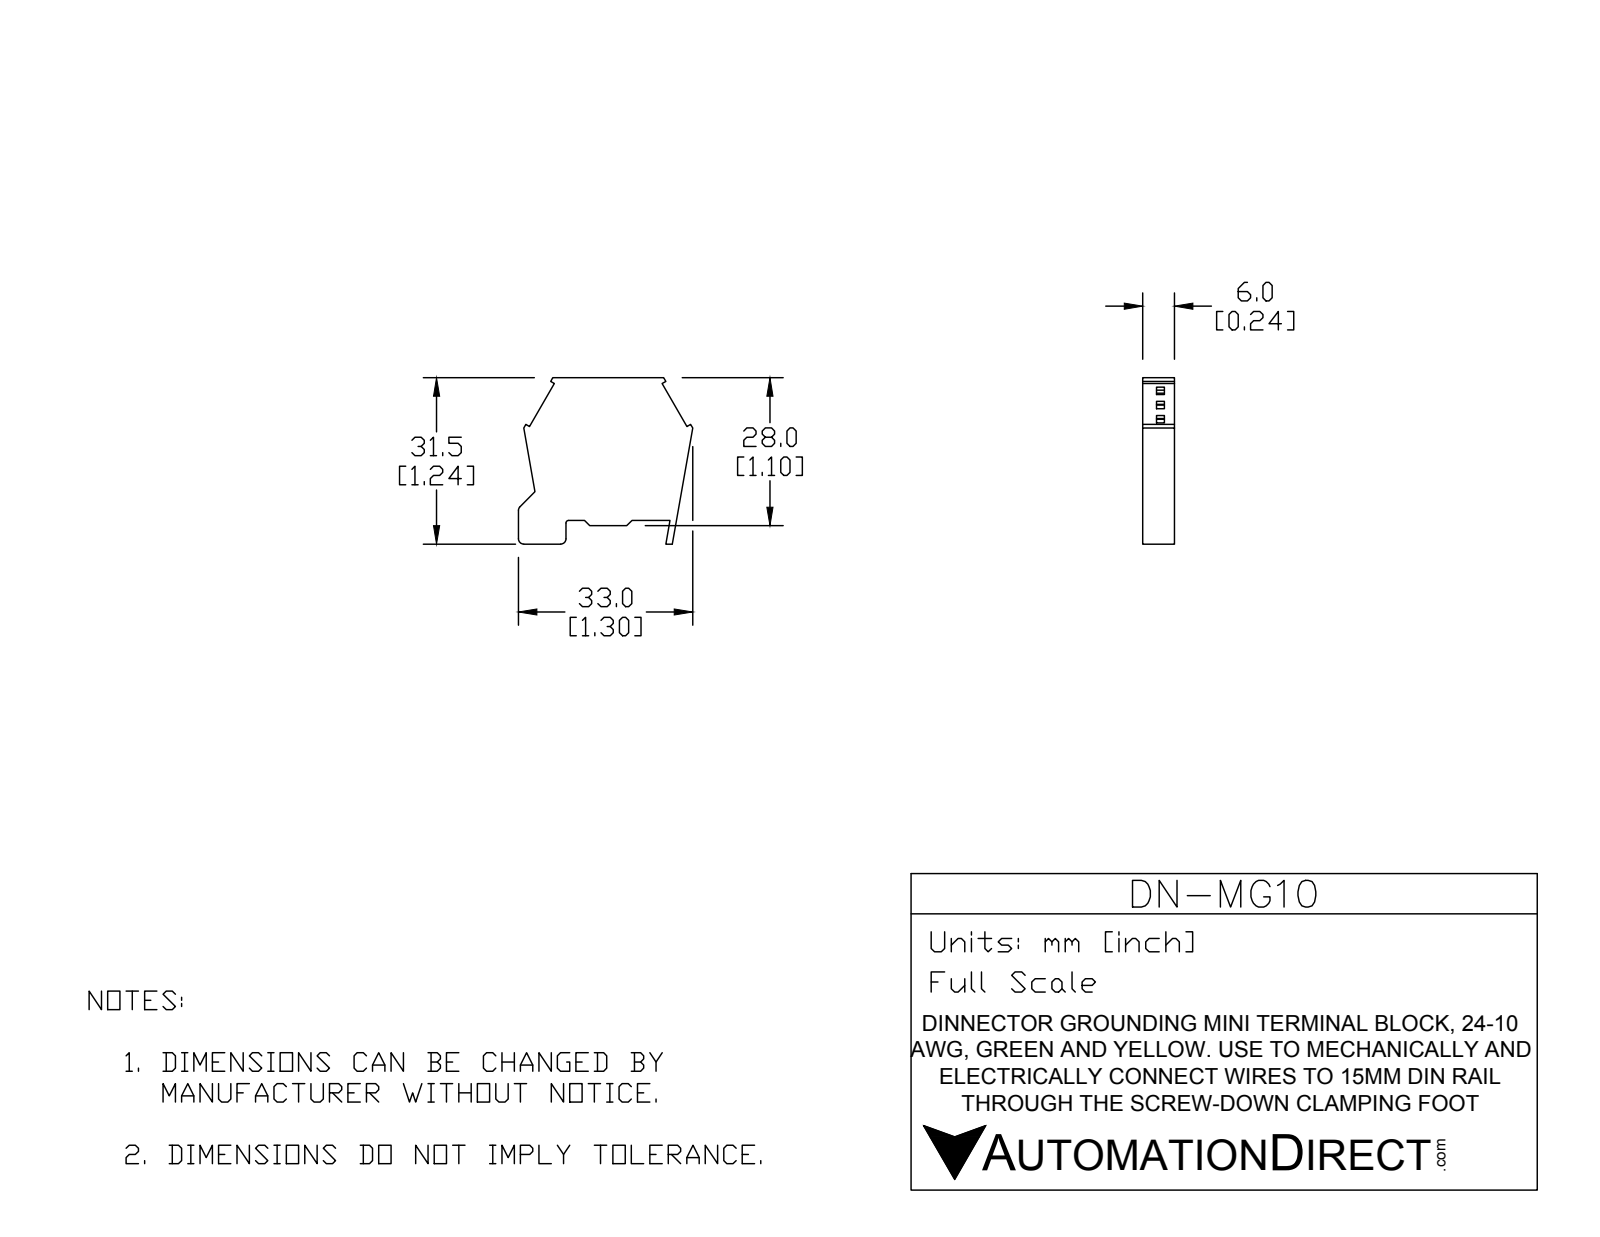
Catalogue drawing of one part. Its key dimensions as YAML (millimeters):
part_name: "43459_DN-MG10"
step_written_by: "SolidWorks 2013 (AUTOMOTIVE_DESIGN)"
units: millimeters
bodies: {solids: 1, faces: 93, planar: 82, cylindrical: 11, other: 0}
overall_size: [33, 31.5, 6]
volume: 4728
surface_area: 2609
round_holes:
  - {diameter: 4, count: 2}
partial_cylinders:
  - {radius: 0.5, count: 3}
  - {radius: 1, count: 3}
face_to_face_distances: [6, 27, 4.5, 31.5, 3.5, 1, 28, 1.2, 1.9, 3.4]
hole_center_spacings: [13]
